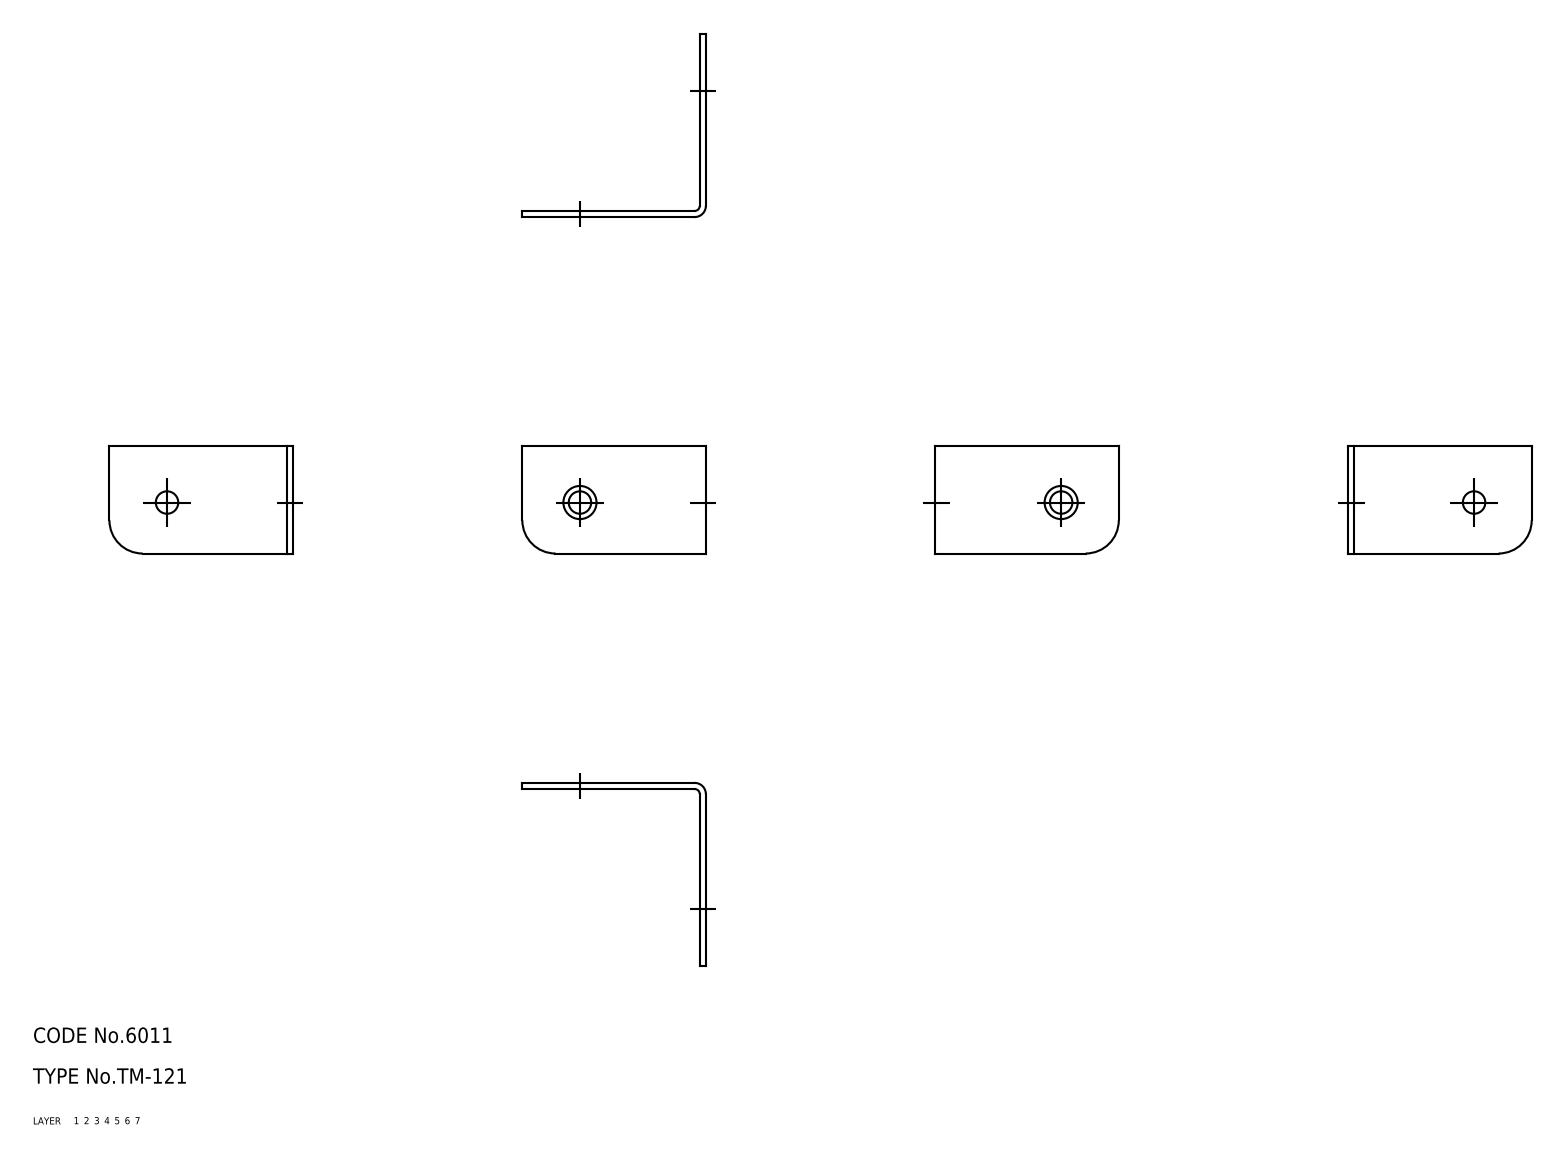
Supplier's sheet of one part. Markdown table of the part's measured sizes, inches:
| quantity | value |
| --- | --- |
| part name | angle |
| STEP written by | CADfix (AUTOMOTIVE_DESIGN) |
| units | inches |
| bodies | 1 solid, 20 faces (0 planar, 0 cylindrical, 20 other) |
| overall size | 1.417 × 1.417 × 0.827 |
| volume | 0.103 in³ |
| surface area | 4.772 in² |
